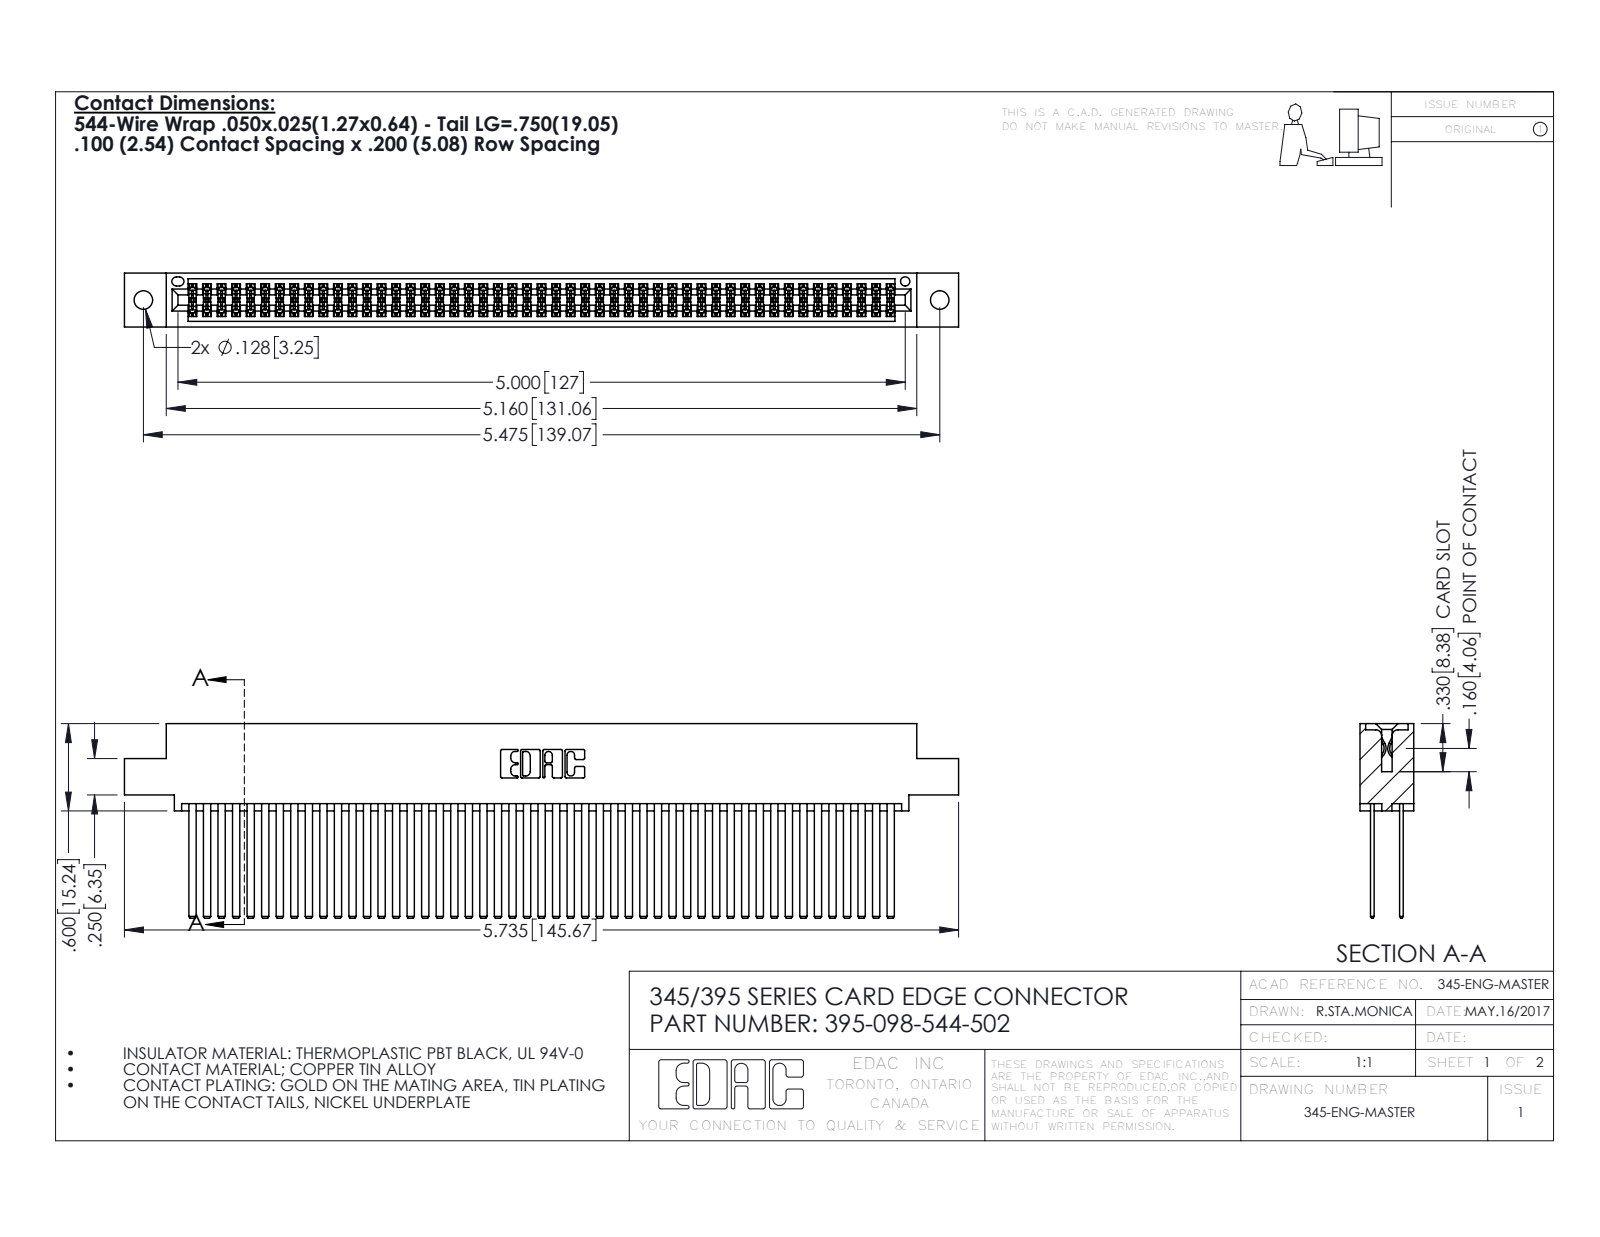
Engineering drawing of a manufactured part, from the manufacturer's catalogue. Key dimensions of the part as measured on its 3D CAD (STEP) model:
Part name (STEP PRODUCT): 395-098-544-502; 345-292-001_345-293-144; 345 Part_0.110 Offset - 0.128 Dia
STEP written by: SolidWorks 2016 (CONFIG_CONTROL_DESIGN)
Units: inches
Bodies: 99 solids, 4442 faces (2926 planar, 1516 cylindrical, 0 other)
Overall size (bounding box): 5.735 × 1.337 × 0.37
Volume: 0.945 in³ · Surface area: 41.64 in²
Round holes (diameter × count): ⌀0.128 ×2, ⌀0.064 ×1
Partial cylindrical surfaces — rounded edges, fillets, slot ends (radius × count): R0.006 ×147, R0.01 ×22, R0.007 ×6, R0.031 ×6, R0.026 ×3, R0.014 ×2, R0.019 ×2, R0.022 ×2
Main face-to-face distances: 0.2, 0.025, 0.298, 0.072, 0.098, 0.272, 0.225, 0.175, 0.37, 0.05
Hole centre spacings: 0.27, 5.239, 5.475
